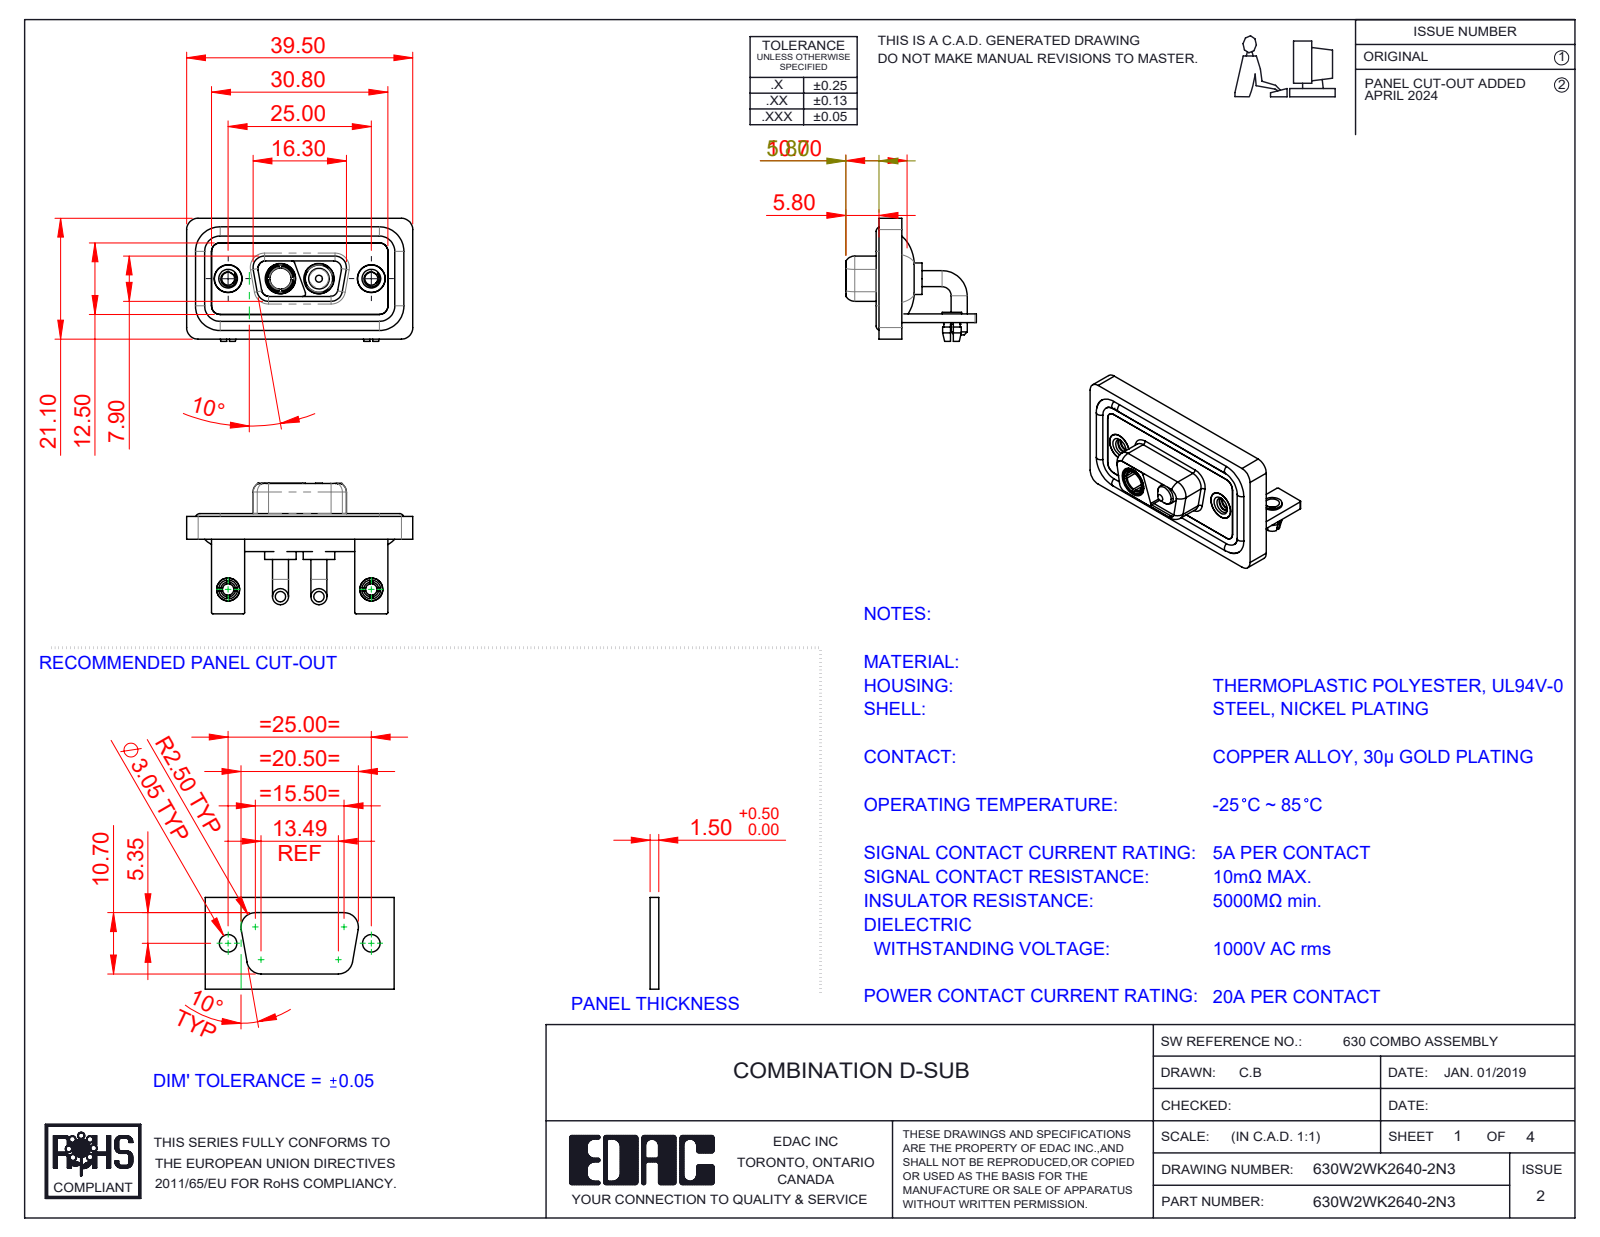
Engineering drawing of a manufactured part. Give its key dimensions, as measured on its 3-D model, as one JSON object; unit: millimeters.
{"part_name": "630Combo Shell Rear_09 Contacts; 630Combo Board Lock_50 Contacts; 630Combo Shell Front_09 Contacts; 630Combo Housing_2WK2 (+6 more)", "step_written_by": "SolidWorks 2023 (CONFIG_CONTROL_DESIGN)", "units": "millimeters", "bodies": {"solids": 15, "faces": 648, "planar": 212, "cylindrical": 291, "other": 145}, "overall_size": [39.5, 22.8, 21.5], "volume_mm3": 5109, "surface_area_mm2": 8440, "round_holes": [[4.85, 4], [2, 2], [2.26, 2], [2.5, 2], [3.2, 2], [4, 2], [4.05, 2], [5, 2], [5.3, 2], [3.7, 1]], "round_bosses_or_shafts": [[2.8, 4], [1.6, 4], [5.5, 2], [5.2, 2], [4.95, 2], [4.8, 2], [4.75, 2], [4, 2]], "partial_cylinders_radius": [[2, 19], [1.5, 18], [0.25, 16], [1.35, 8], [1.6, 8], [0.5, 7], [0.6, 4], [0.65, 4]], "face_to_face_distances": [0.4, 2.9, 1.5, 1.1, 3.7, 1.8, 0.8, 2.5, 1.6, 3.1], "hole_center_spacings": [9.14, 15.86, 25, 6.72]}
